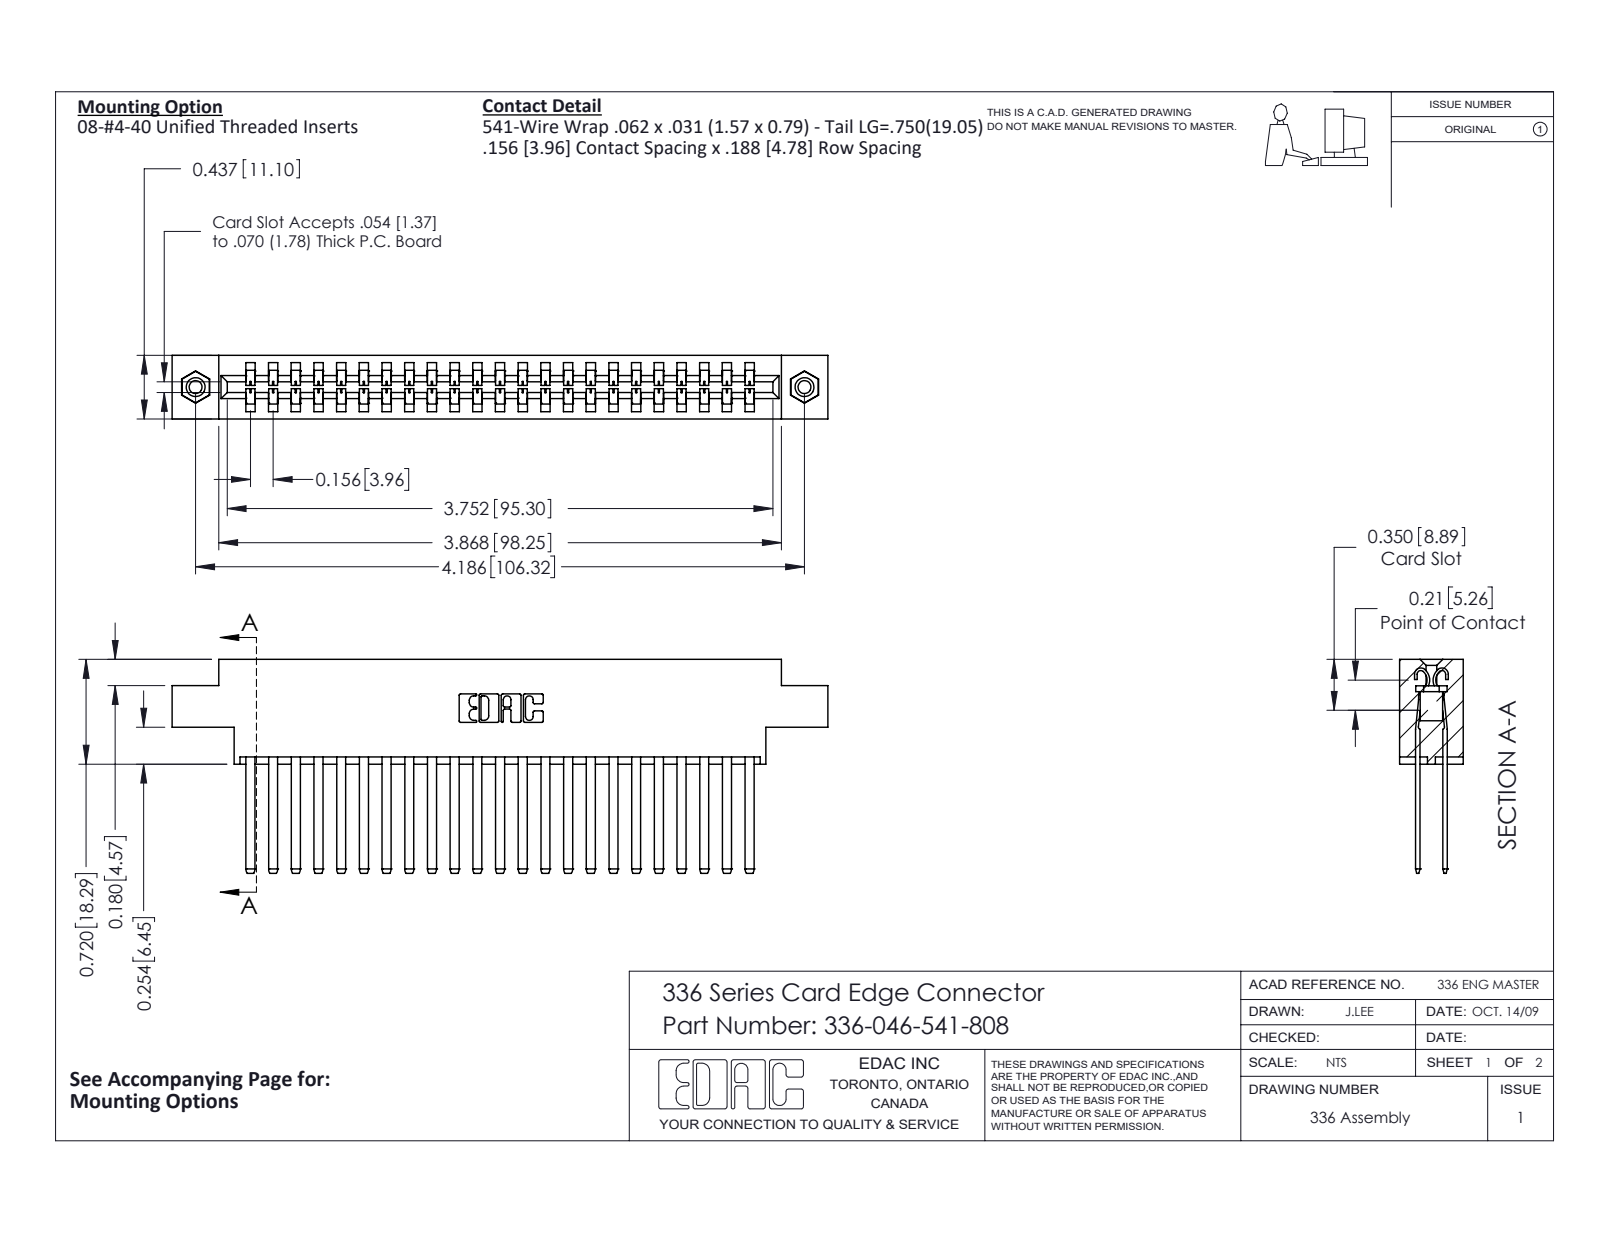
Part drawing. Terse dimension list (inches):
name: 345-250-001_345-250-003-102; 336-290-001_336-290-541; 336 Part_Offset - .156 Dia - TI; 336-046-541-808
written by: SolidWorks 2020 (CONFIG_CONTROL_DESIGN)
unit: in
bodies: 49 solids, 2110 faces (1302 planar, 792 cylindrical, 16 other)
size: 4.509 × 1.47 × 0.437
volume: 1.041 in³; area: 33.39 in²
holes: 2× ⌀0.089, 2× ⌀0.125, 2× ⌀0.156
bosses: 2× ⌀0.155
rounds: 92× R0.004, 46× R0.056, 22× R0.01, 6× R0.007, 6× R0.031, 4× R0.022, 4× R0.04, 3× R0.026
face distances: 0.188, 0.328, 0.14, 0.297, 0.109, 0.031, 0.437, 0.033, 0.156, 0.181
hole spacings: 4.186
